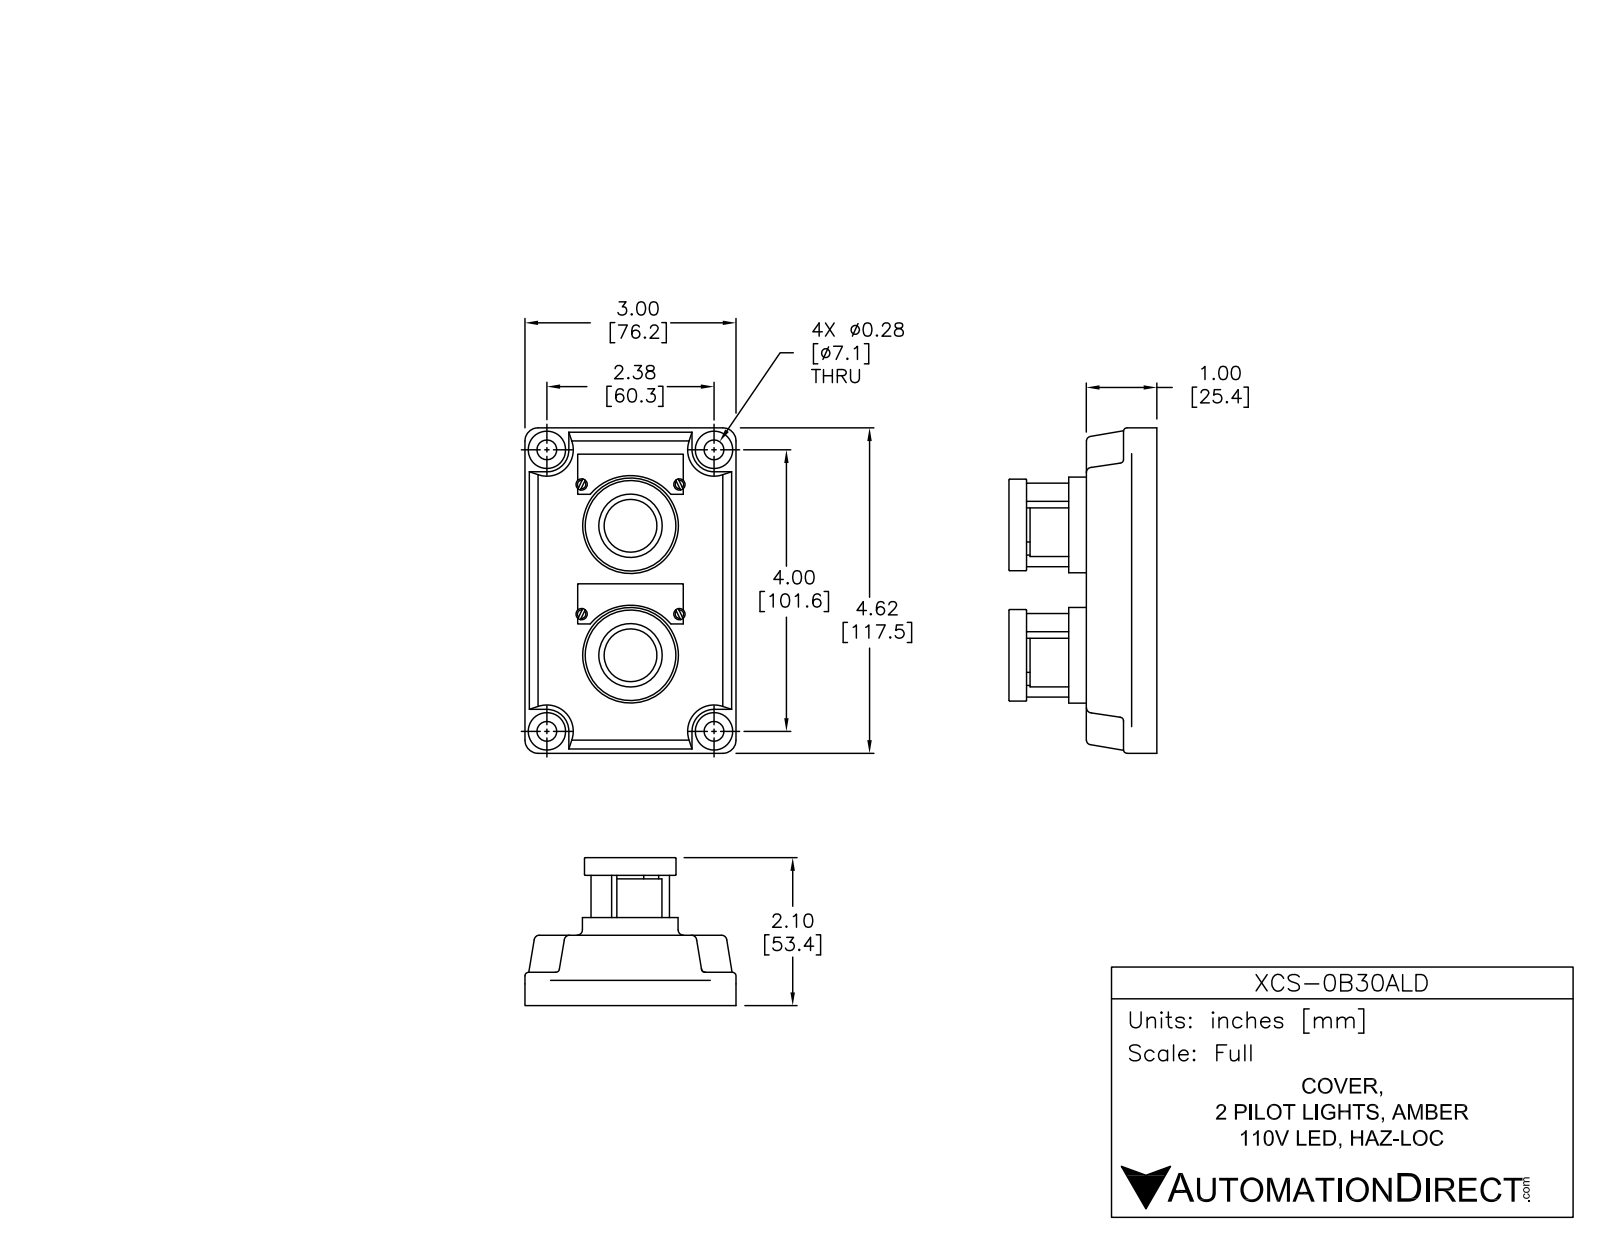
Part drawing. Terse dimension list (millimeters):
name: XCS-0B30ALD
written by: SolidWorks 2015 (AUTOMOTIVE_DESIGN)
unit: mm
bodies: 28 solids, 579 faces (219 planar, 195 cylindrical, 165 other)
size: 117.47 × 79.05 × 70.32
volume: 165 224 mm³; area: 66 972 mm²
holes: 4× ⌀7.24, 2× ⌀6.3, 2× ⌀17.5, 2× ⌀22.61, 2× ⌀32
bosses: 8× ⌀4.06, 4× ⌀11.6, 4× ⌀6.35, 2× ⌀36.83, 2× ⌀31.75, 2× ⌀22, 2× ⌀15.25, 2× ⌀10
rounds: 16× R1.5, 12× R2, 8× R0.76, 8× R3, 8× R6.35, 6× R1.4, 6× R1.52, 4× R0.51
face distances: 26, 1.5, 12.66, 13.34, 11.63, 24.29, 37.63, 10.13, 22.79, 36.13
hole spacings: 47.5, 0.45, 40.24, 40.32, 80.24, 80.36, 101.6, 117.84
